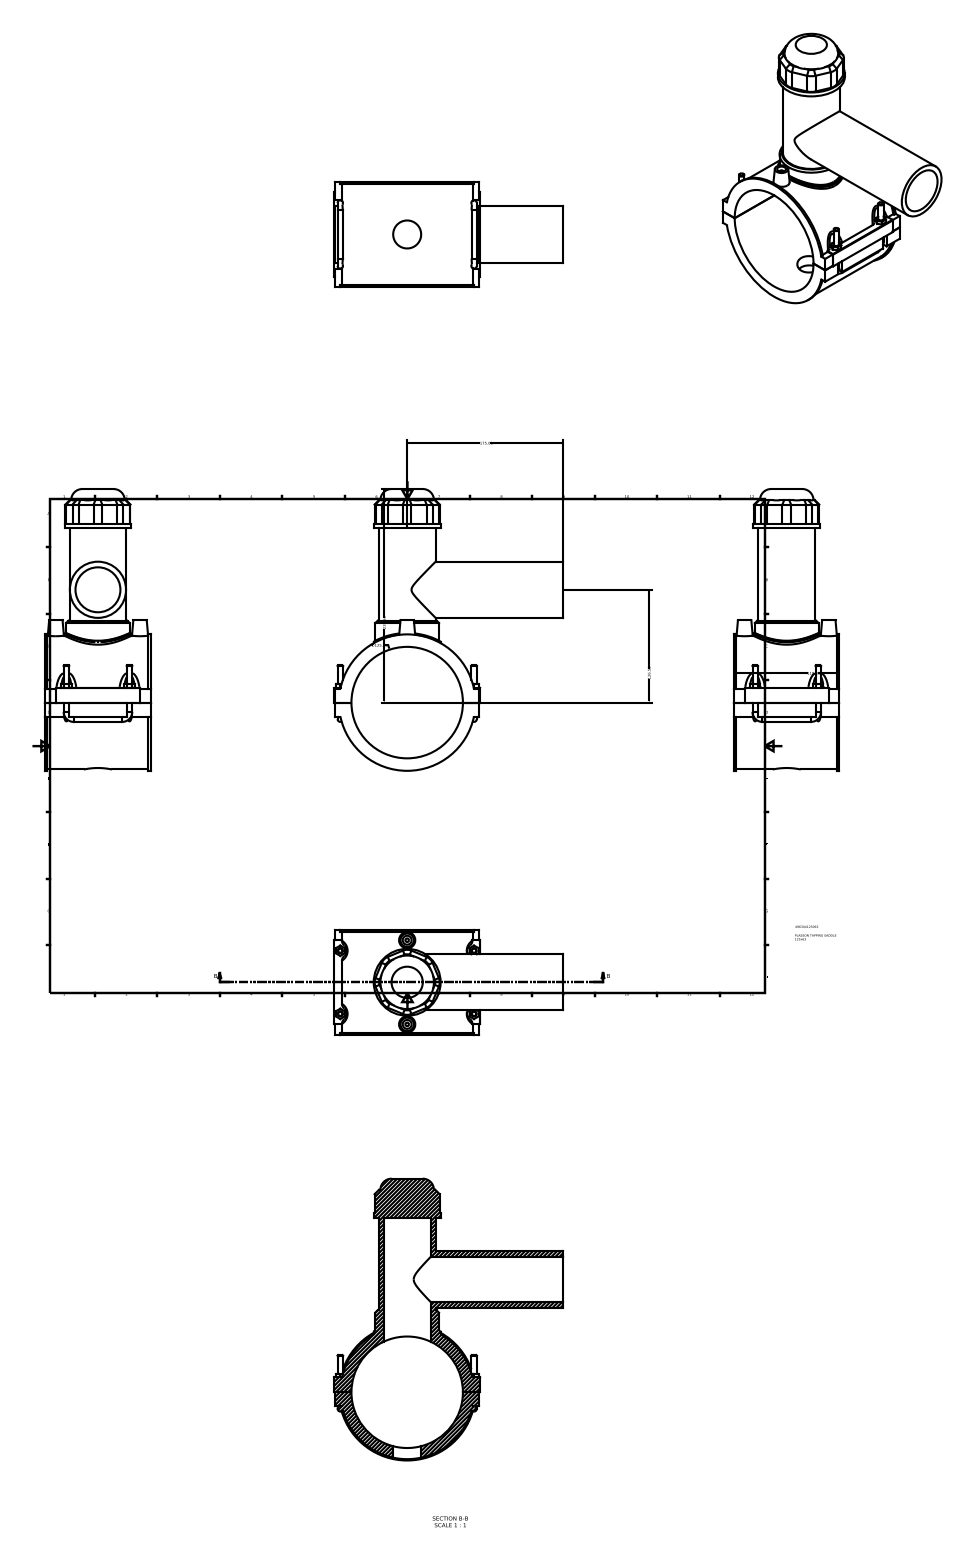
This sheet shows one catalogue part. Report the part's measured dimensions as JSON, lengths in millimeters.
{"part_name": "496304125063", "step_written_by": "Autodesk Inventor 2015 (AUTOMOTIVE_DESIGN)", "units": "millimeters", "bodies": {"solids": 1, "faces": 211, "planar": 126, "cylindrical": 56, "other": 29}, "overall_size": [316, 257, 118], "volume_mm3": 1120000, "surface_area_mm2": 244318, "round_holes": [[10, 2], [31.36, 1], [50.4, 1], [52.5, 1], [125, 1]], "round_bosses_or_shafts": [[6, 4], [4, 2], [153, 1], [150, 1], [75, 1], [71.25, 1], [63.75, 1], [63, 1]], "partial_cylinders_radius": [[12.5, 8], [3, 6], [7.5, 4], [0.5, 1], [78, 1]], "face_to_face_distances": [118, 195.3, 195.2, 1, 163, 162, 15.57, 15.67, 210.87, 32.25], "hole_center_spacings": [47.2, 94.4]}
